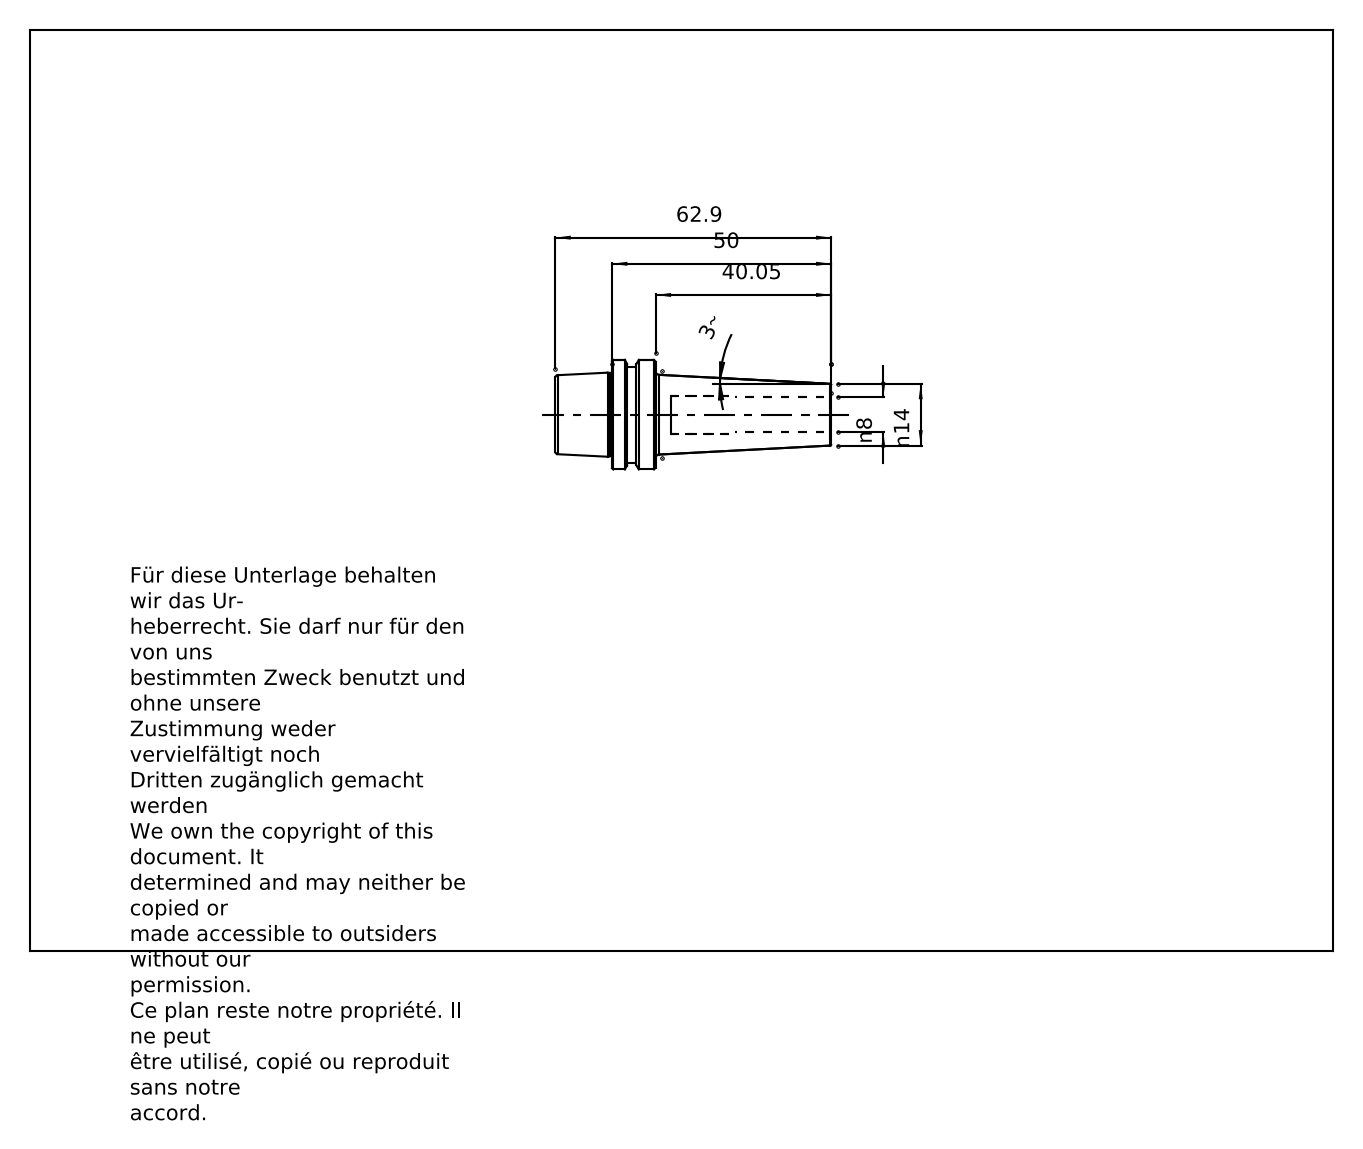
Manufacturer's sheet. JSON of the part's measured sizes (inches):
{"part_name": "E25-180-08", "step_written_by": "PRO/ENGINEER BY PARAMETRIC TECHNOLOGY CORPORATION, 2010430 (CONFIG_CONTROL_DESIGN)", "units": "inches", "bodies": {"solids": 1, "faces": 60, "planar": 8, "cylindrical": 16, "other": 36}, "overall_size": [2.476, 0.984, 0.984], "volume_in3": 0.68, "surface_area_in2": 9.855, "round_holes": [[0.315, 1], [0.553, 1], [0.648, 1]], "round_bosses_or_shafts": [[0.984, 1], [0.864, 1], [0.746, 1]], "face_to_face_distances": [0.157, 0.234, 0.392, 1.969, 1.734, 1.577, 0.508, 0.742, 0.9, 2.476]}
